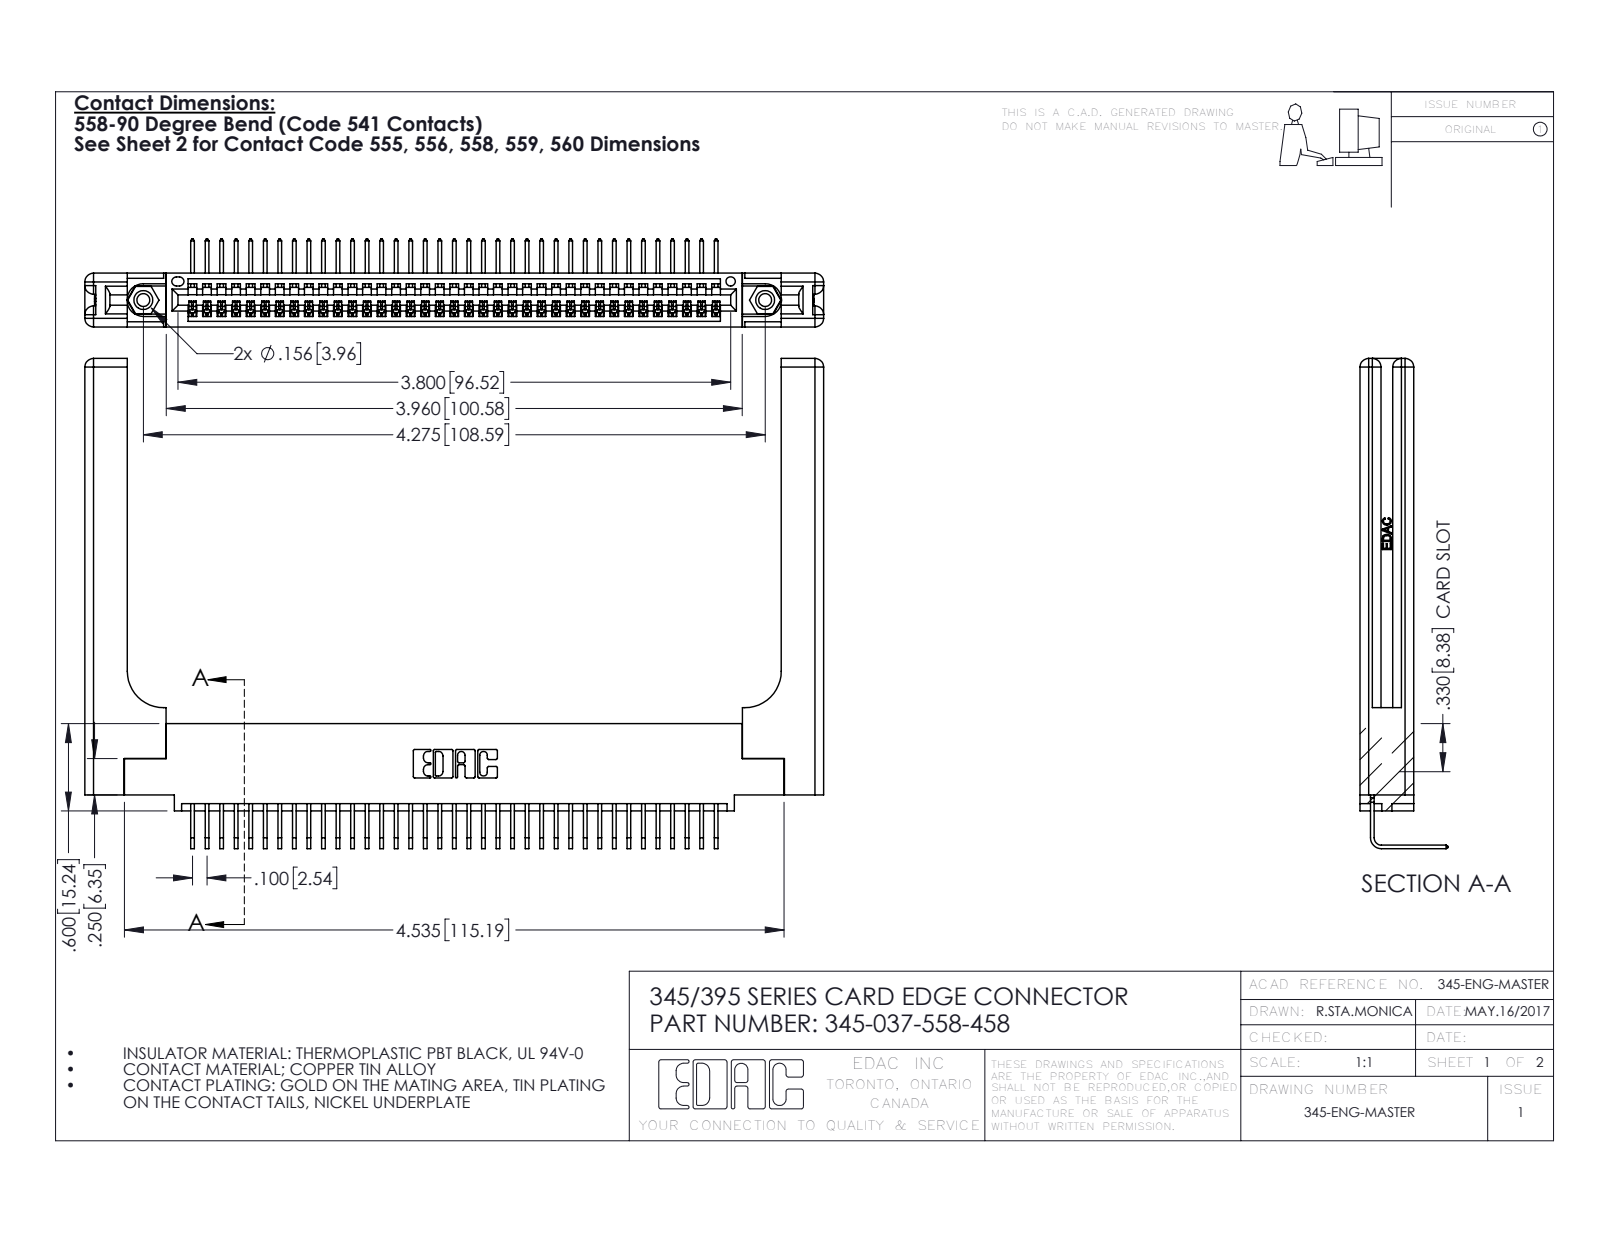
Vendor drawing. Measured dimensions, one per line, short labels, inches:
name: 345-037-558-458; 345-220-058_345-220-058; 345-292-001_558 Tail - 2; 345-250-001_345-250-001-102 (+1 more)
written by: SolidWorks 2016 (CONFIG_CONTROL_DESIGN)
unit: in
bodies: 42 solids, 2606 faces (1786 planar, 760 cylindrical, 60 other)
size: 5.079 × 3.369 × 0.605
volume: 1.267 in³; area: 34.63 in²
holes: 2× ⌀0.089, 2× ⌀0.125, 2× ⌀0.156, 1× ⌀0.064
bosses: 2× ⌀0.155
rounds: 74× R0.006, 22× R0.01, 16× R0.06, 6× R0.007, 6× R0.031, 3× R0.026, 2× R0.03, 2× R0.031
face distances: 0.37, 0.072, 0.298, 0.098, 0.272, 0.025, 0.2, 0.148, 0.15, 0.225
hole spacings: 0.27, 4.039, 4.275
